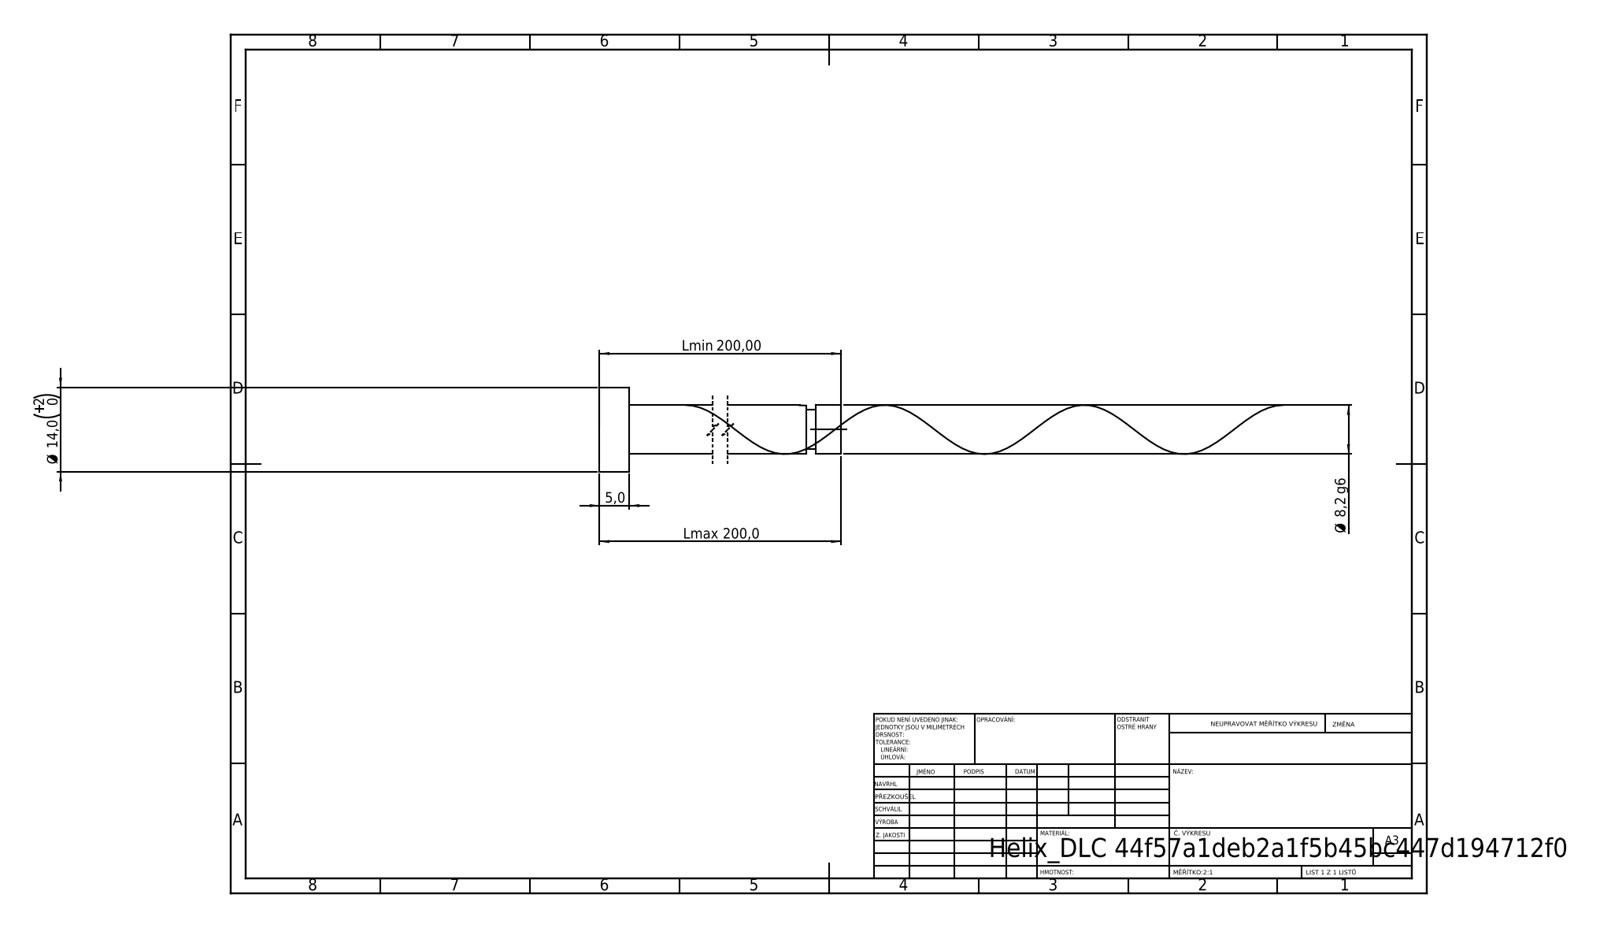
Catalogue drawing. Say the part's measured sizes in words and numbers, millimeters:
Its 3-D file was written by "SolidWorks 2019 (CONFIG_CONTROL_DESIGN)". It is 1 solid with 21 faces: 6 planar, 14 cylindrical and 1 other. Overall it measures 200 by 14 by 14 millimeters. Its volume is 10 935 cubic millimeters and its surface area 5 688 square millimeters. Round bosses or shafts: 1 of diameter 14, 1 of diameter 8.2, 1 of diameter 6.56. The main face-to-face distances are 5, 200, 195, 195.81, 190.81, 4.19, 194.17, 189.17, 1.64, 5.83.
